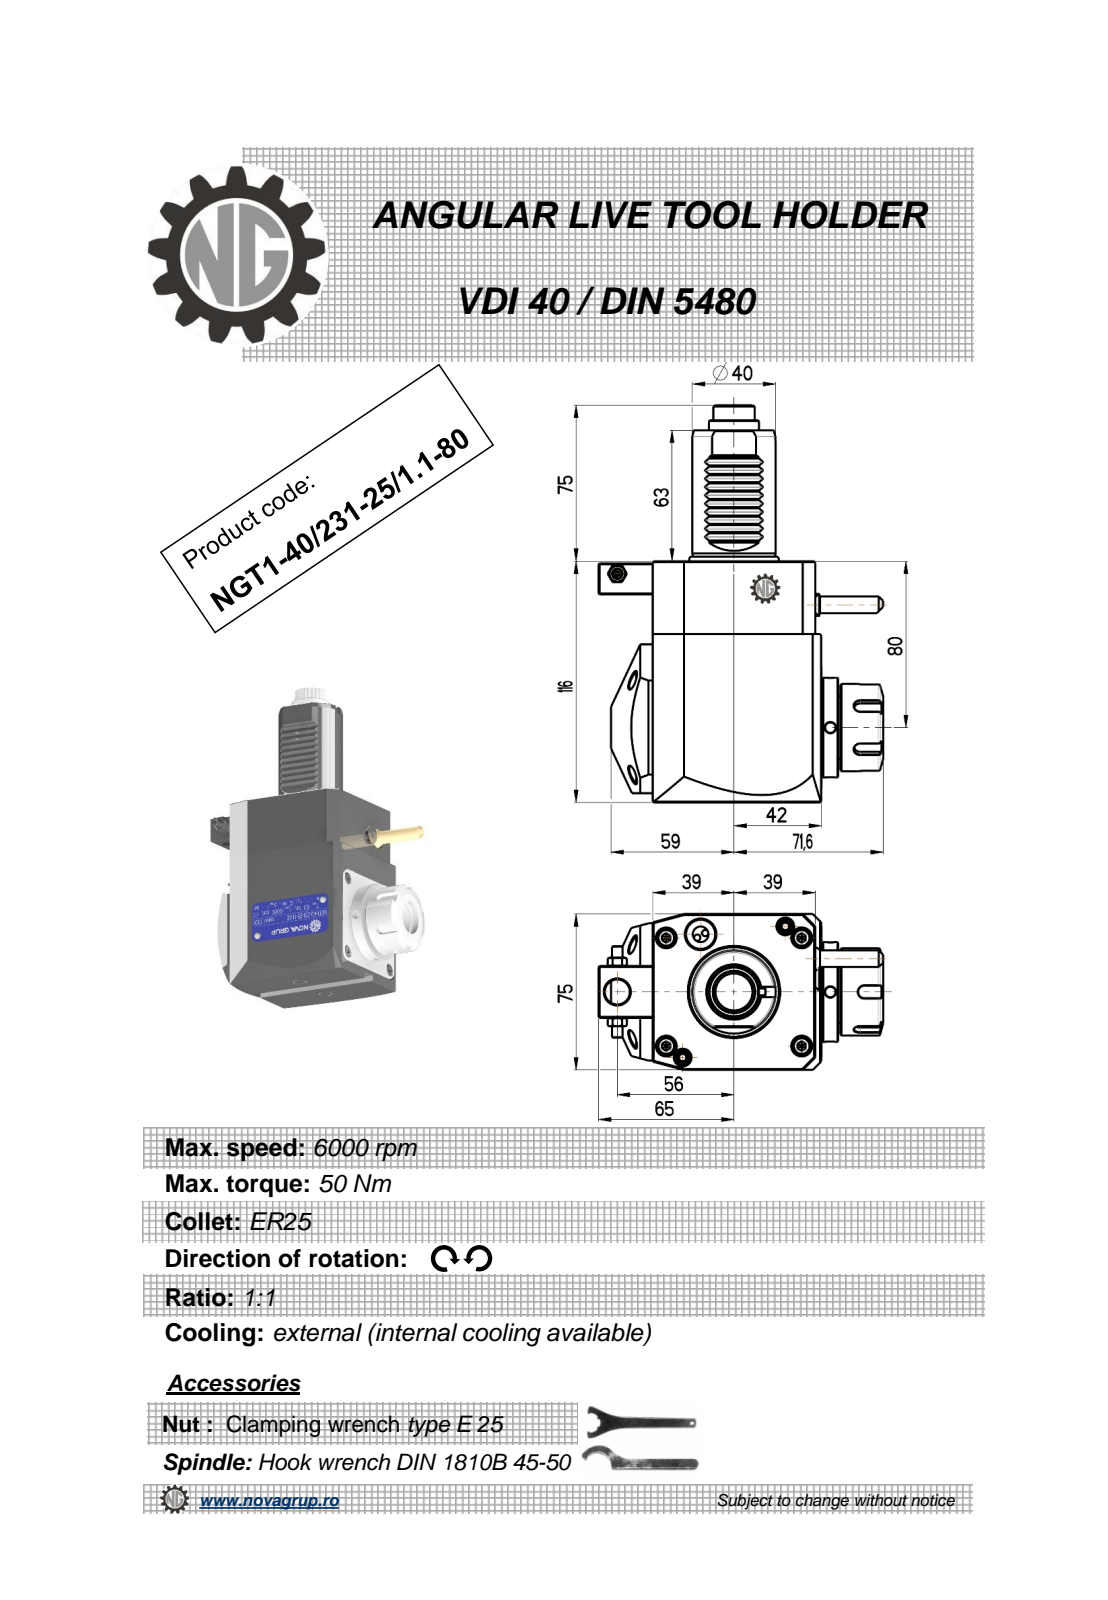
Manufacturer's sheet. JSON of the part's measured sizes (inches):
{"part_name": "NGT1_40_231_25_1_1_80", "step_written_by": "PRO/ENGINEER BY PARAMETRIC TECHNOLOGY CORPORATION, 2010280 (CONFIG_CONTROL_DESIGN)", "units": "inches", "bodies": {"solids": 1, "faces": 555, "planar": 194, "cylindrical": 185, "other": 176}, "overall_size": [7.52, 5.378, 3.016], "volume_in3": 52.79, "surface_area_in2": 108.4, "round_holes": [[0.197, 3], [0.118, 1], [0.165, 1], [0.374, 1], [0.472, 1], [0.799, 1]], "round_bosses_or_shafts": [[1.89, 1], [1.654, 1], [1.575, 1], [1.476, 1], [1.299, 1], [0.945, 1], [0.441, 1], [0.353, 1]], "partial_cylinders_radius": [[0.082, 48], [0.01, 12], [0.012, 10], [0.009, 6], [0.118, 5], [0.357, 1], [0.391, 1], [0.591, 1]], "face_to_face_distances": [2.953, 4.567, 3.189, 0.118, 3.071, 3.181, 0.11, 0.295, 0.02, 0.433], "hole_center_spacings": [0.799, 2.407, 2.815, 4.026, 4.969]}
